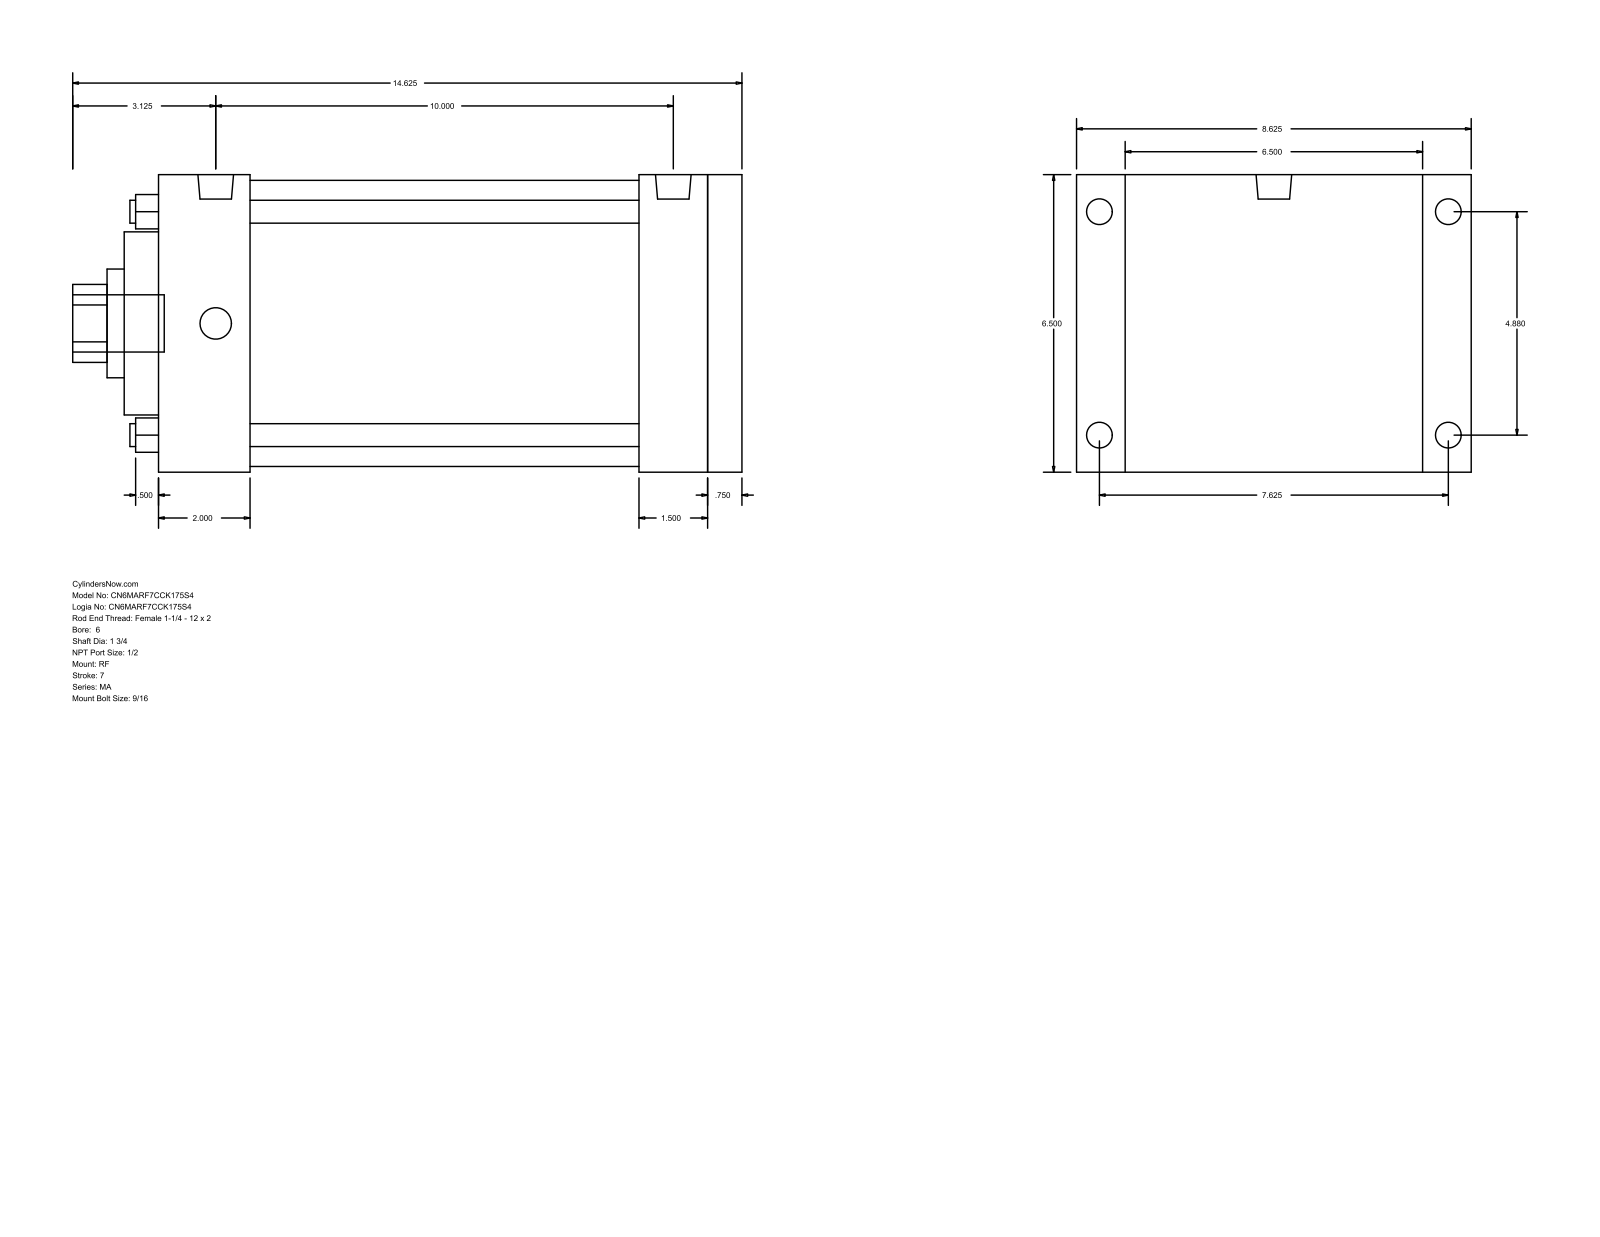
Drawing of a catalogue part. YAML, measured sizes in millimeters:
part_name: "MA_RF__0600_1.75"
step_written_by: "GSSL Pune (CONFIG_CONTROL_DESIGN)"
units: millimeters
bodies: {solids: 0, faces: 94, planar: 65, cylindrical: 29, other: 0}
overall_size: [371.48, 219.07, 165.1]
round_holes:
  - {diameter: 12.7, count: 4}
  - {diameter: 44.45, count: 1}
  - {diameter: 60.33, count: 1}
  - {diameter: 101.6, count: 1}
  - {diameter: 158.75, count: 1}
round_bosses_or_shafts:
  - {diameter: 17.46, count: 4}
  - {diameter: 14.29, count: 4}
  - {diameter: 19.77, count: 2}
  - {diameter: 31.75, count: 1}
partial_cylinders:
  - {radius: 21.63, count: 1}
face_to_face_distances: [165.1, 323.86, 19.05, 304.81, 50.8, 254.01, 273.06, 266.7, 215.9, 38.11]
hole_center_spacings: [87.65, 123.96, 175.31]
